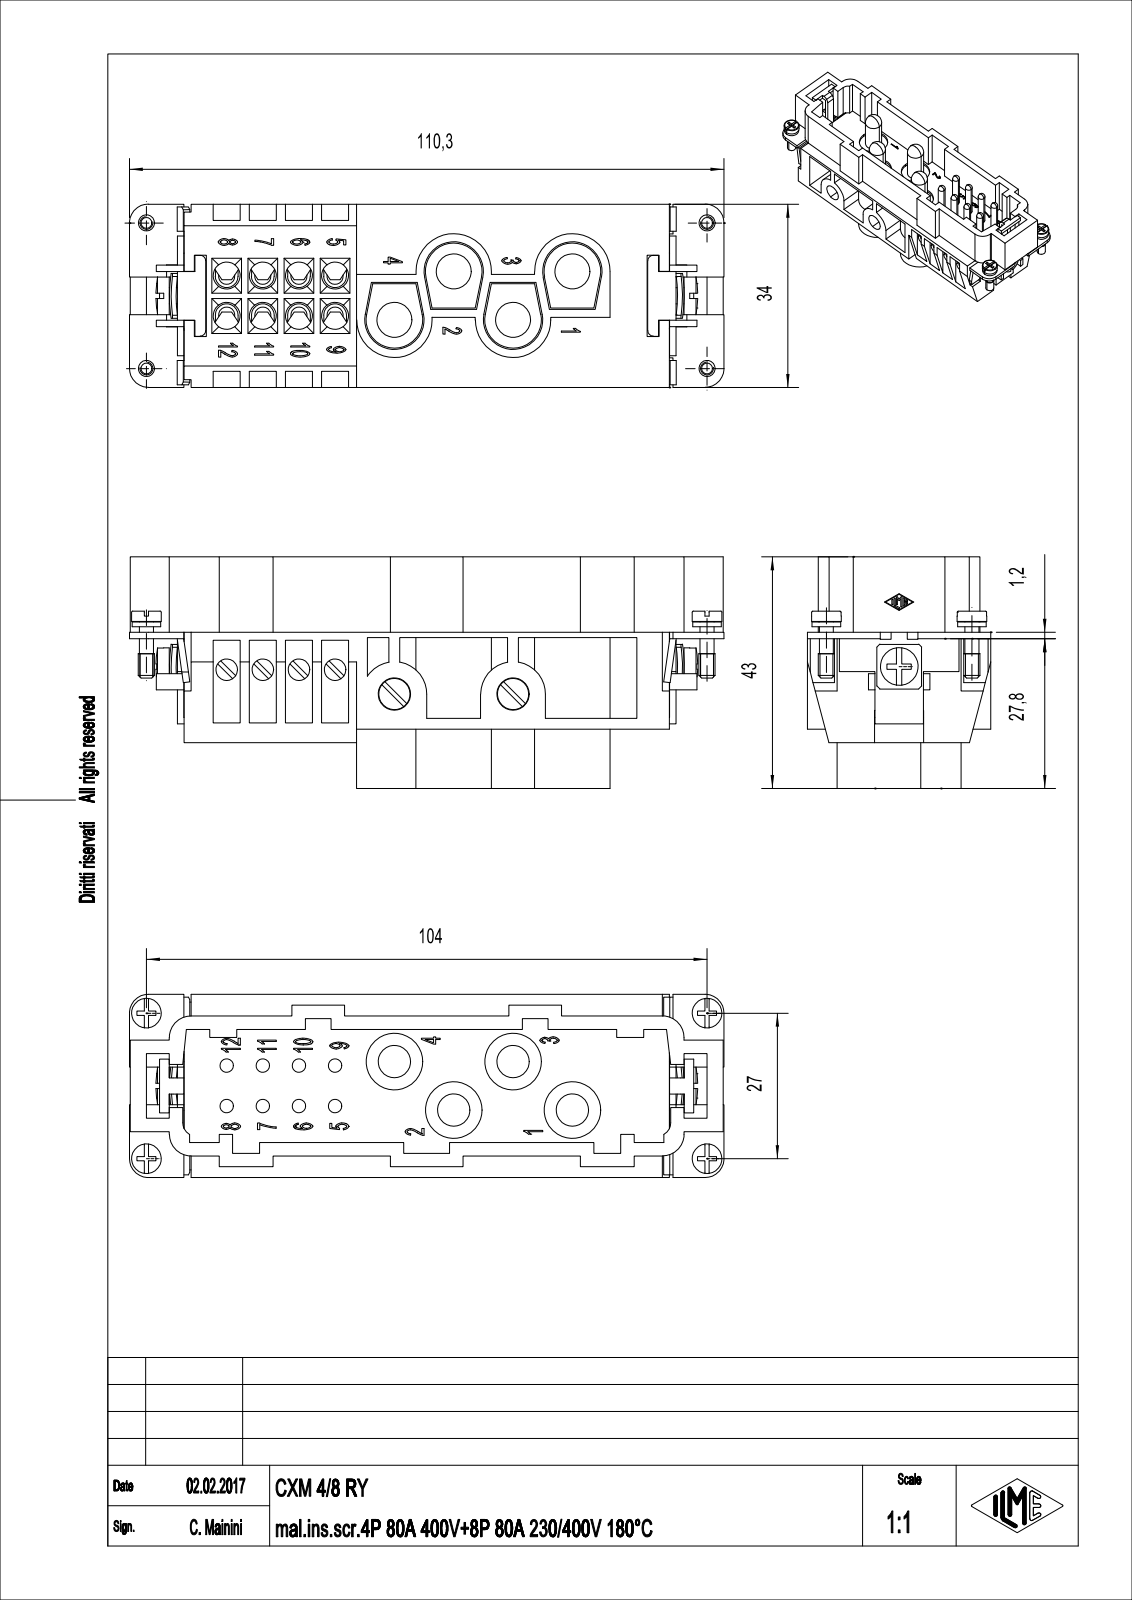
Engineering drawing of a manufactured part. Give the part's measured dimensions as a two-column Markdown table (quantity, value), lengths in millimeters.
| quantity | value |
| --- | --- |
| part name | CXM_4-8_RY |
| STEP written by | PTC Creo Elements/Direct Modeling 19.0E 27-Jun-2016 (C) Parametric Technology GmbH (AUTOMOTIVE_DESIGN) |
| units | millimeters |
| bodies | 5 solids, 1677 faces (1058 planar, 343 cylindrical, 276 other) |
| overall size | 110.3 × 43 × 34 |
| volume | 55 884 mm³ |
| surface area | 43 654 mm² |
| round holes (diameter × count) | 3 × 8, 5 × 8, 4 × 4, 6 × 4, 6.5 × 4, 3.24 × 1 |
| round bosses / shafts (diameter × count) | 2.5 × 8, 10.5 × 4, 6 × 4, 5.8 × 4, 5.5 × 4, 5.3 × 4, 3 × 4, 2.6 × 4 |
| partial cylindrical surfaces (radius × count) | 0.1 × 14, 2.1 × 12, 5.5 × 5, 1 × 4, 3.5 × 4, 4 × 4, 6 × 4, 7 × 4 |
| main face-to-face distances | 2, 6.5, 2.5, 1, 4.5, 18, 21, 17, 23.5, 13 |
| hole center spacings | 6.7, 13.4, 9.95, 20.1, 7.35, 15.28, 9.84, 10.06 |
